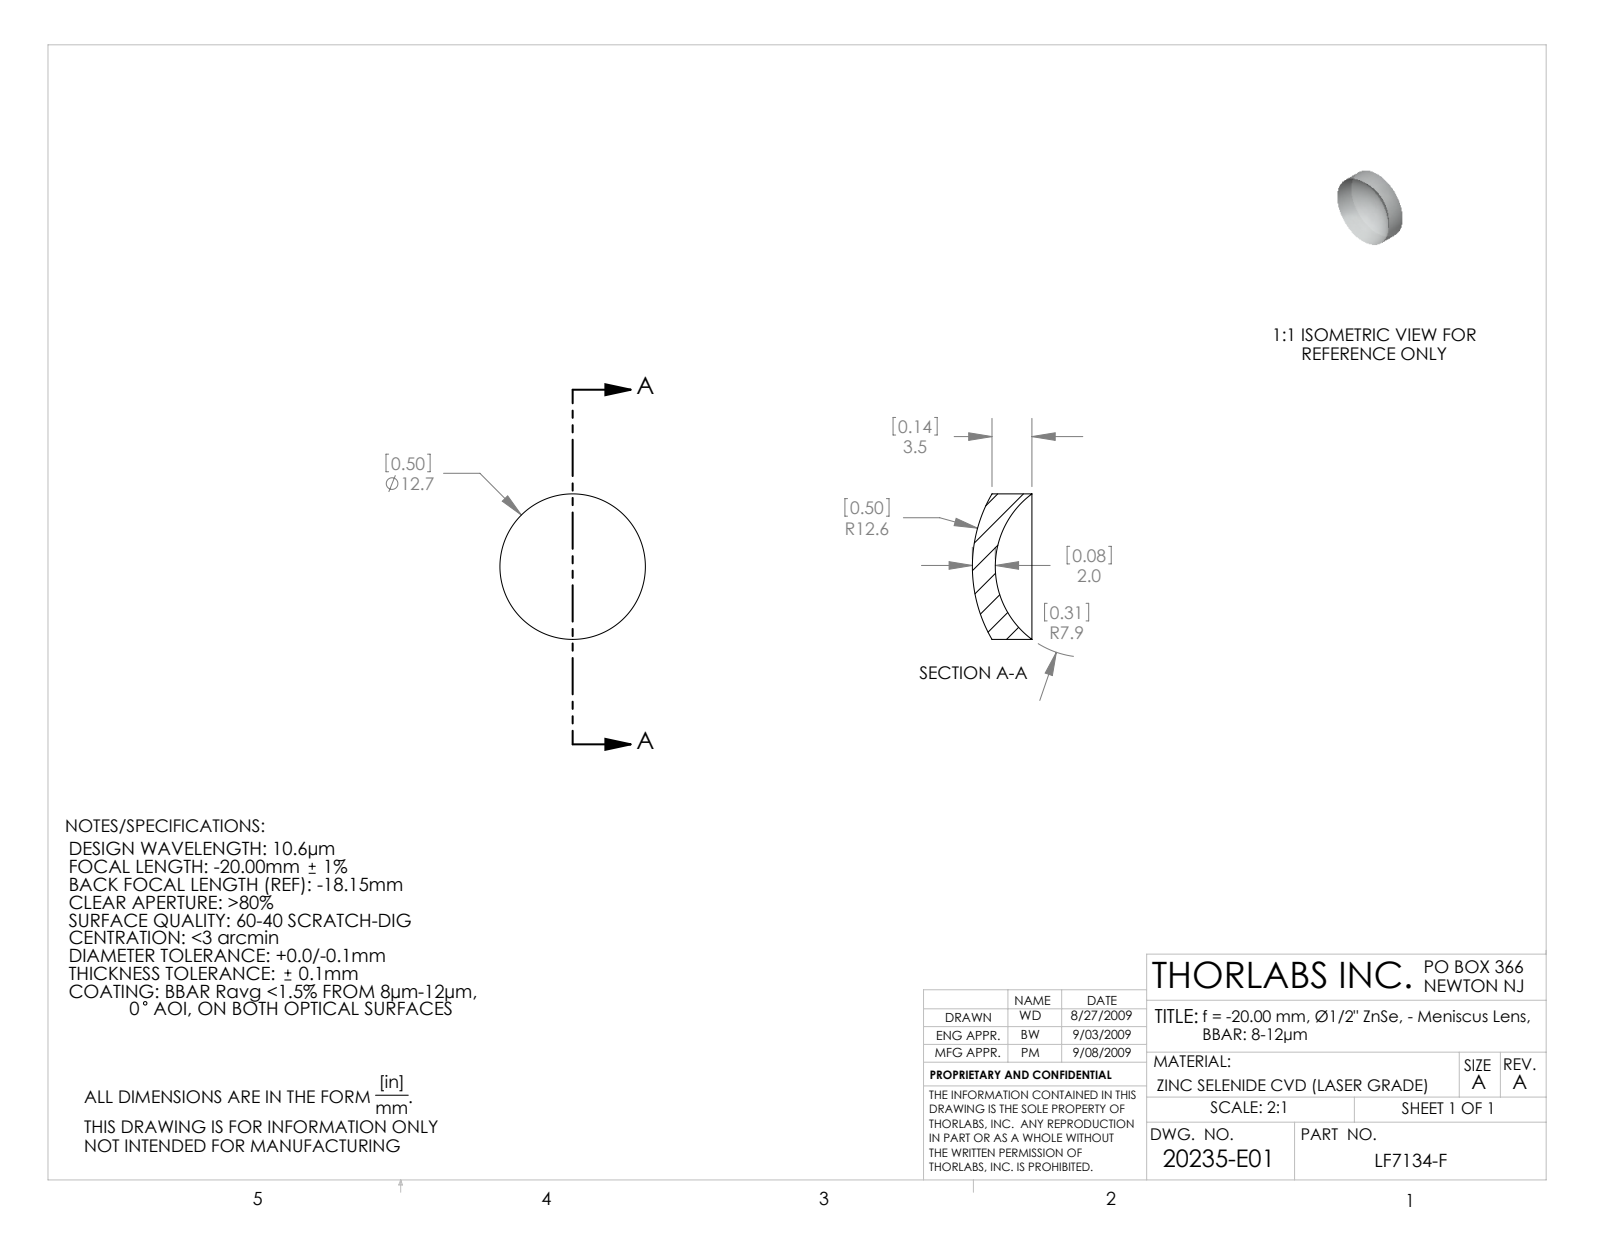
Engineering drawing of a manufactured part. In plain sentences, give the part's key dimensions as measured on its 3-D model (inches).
The part is named "20235-E0W". Its 3-D file was written by "SolidWorks 2007 (CONFIG_CONTROL_DESIGN)". It is 1 solid with 6 faces: 0 planar, 2 cylindrical and 4 other. Overall it measures 0.5 by 0.5 by 0.205 inches. Its volume is 0.02 cubic inches and its surface area 0.673 square inches. Round bosses or shafts: 1 of diameter 0.5.
